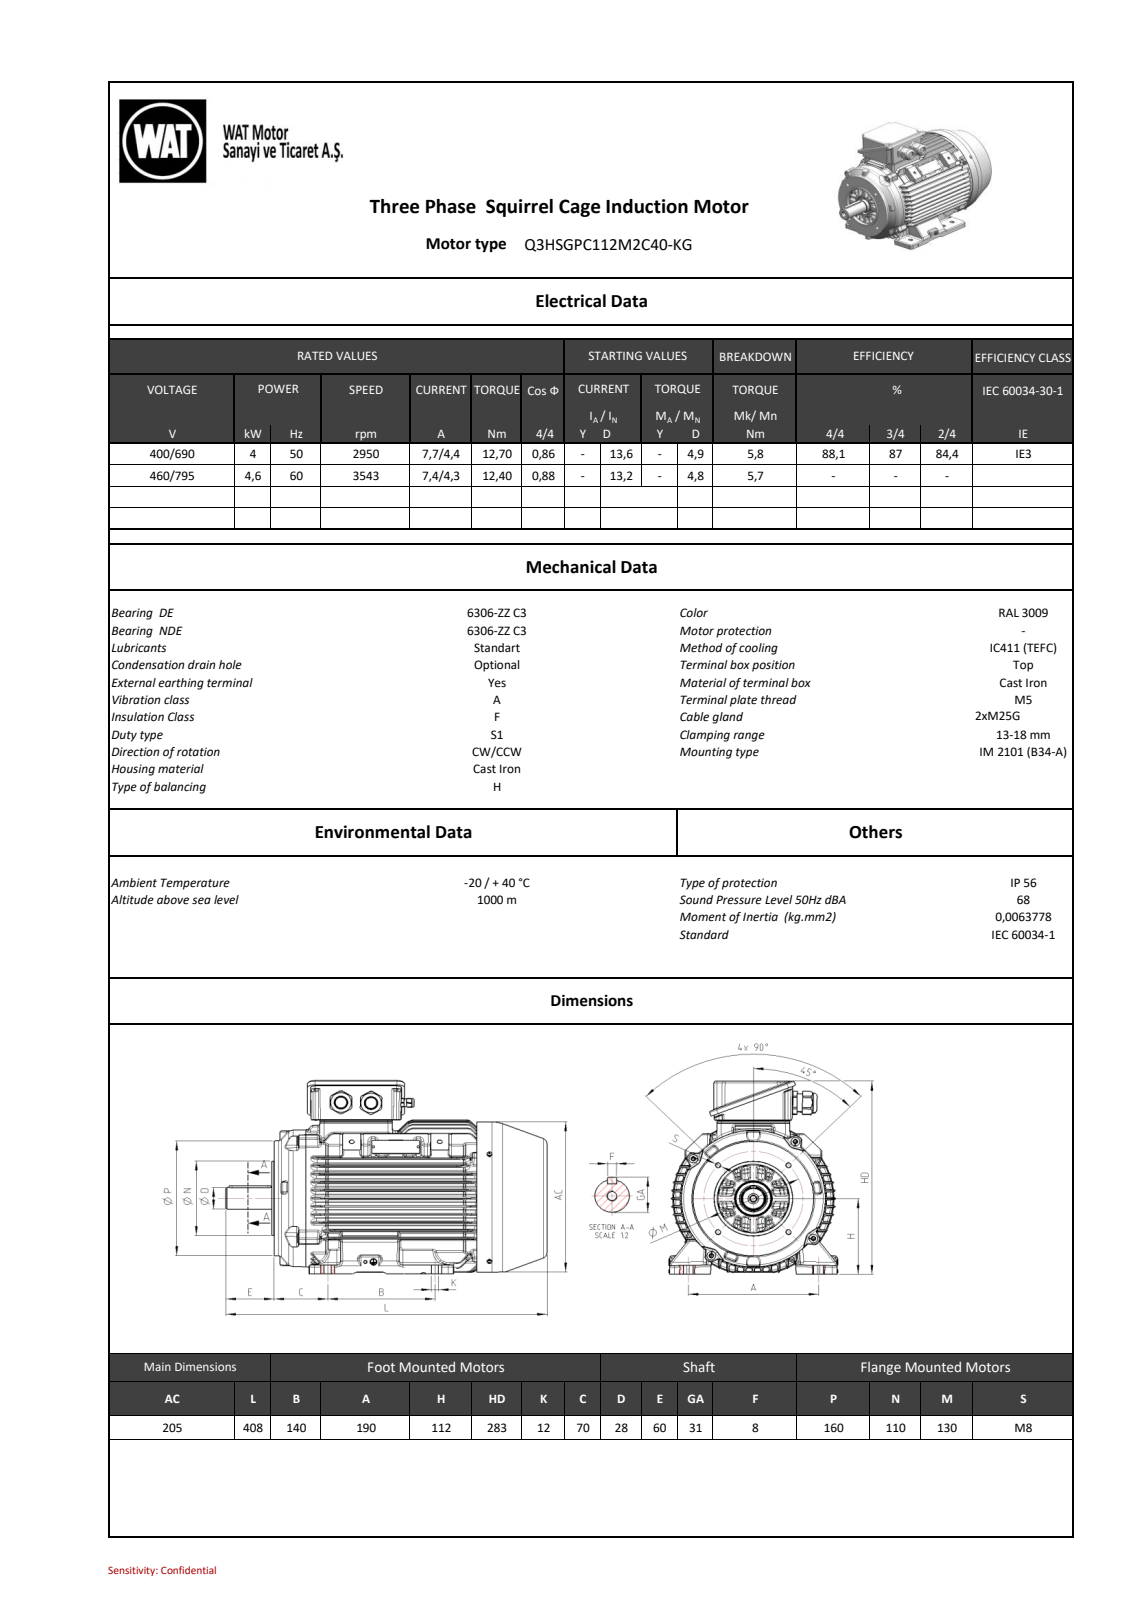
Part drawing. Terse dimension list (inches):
name: 26000A30F4D8rp25
written by: SIEMENS PLM Software NX 11.0 (AUTOMOTIVE_DESIGN)
unit: in
bodies: 0 solids, 5210 faces (949 planar, 1360 cylindrical, 2901 other)
size: 16.063 × 11.121 × 9.748
holes: 8× ⌀0.197, 6× ⌀0.268, 2× ⌀0.098, 1× ⌀0.165, 1× ⌀0.256, 1× ⌀0.26, 1× ⌀0.335, 1× ⌀0.394, 1× ⌀0.413, 1× ⌀1.709, 1× ⌀1.717, 1× ⌀7.756
bosses: 8× ⌀0.394, 4× ⌀0.472, 4× ⌀0.341, 4× ⌀0.315, 4× ⌀0.157, 2× ⌀1.244, 2× ⌀0.787, 1× ⌀7.874
rounds: 279× R0.157, 160× R0.118, 113× R0.059, 41× R0.071, 37× R0.039, 36× R0.079, 30× R0.197, 28× R0.236
face distances: 0.533, 0.536, 1.069, 1.608, 1.075, 0.539, 3.104, 2.567, 2.035, 0.543
hole spacings: 1.097, 3.524, 3.979, 4.7, 4.983, 6.06, 1.223, 2.559
